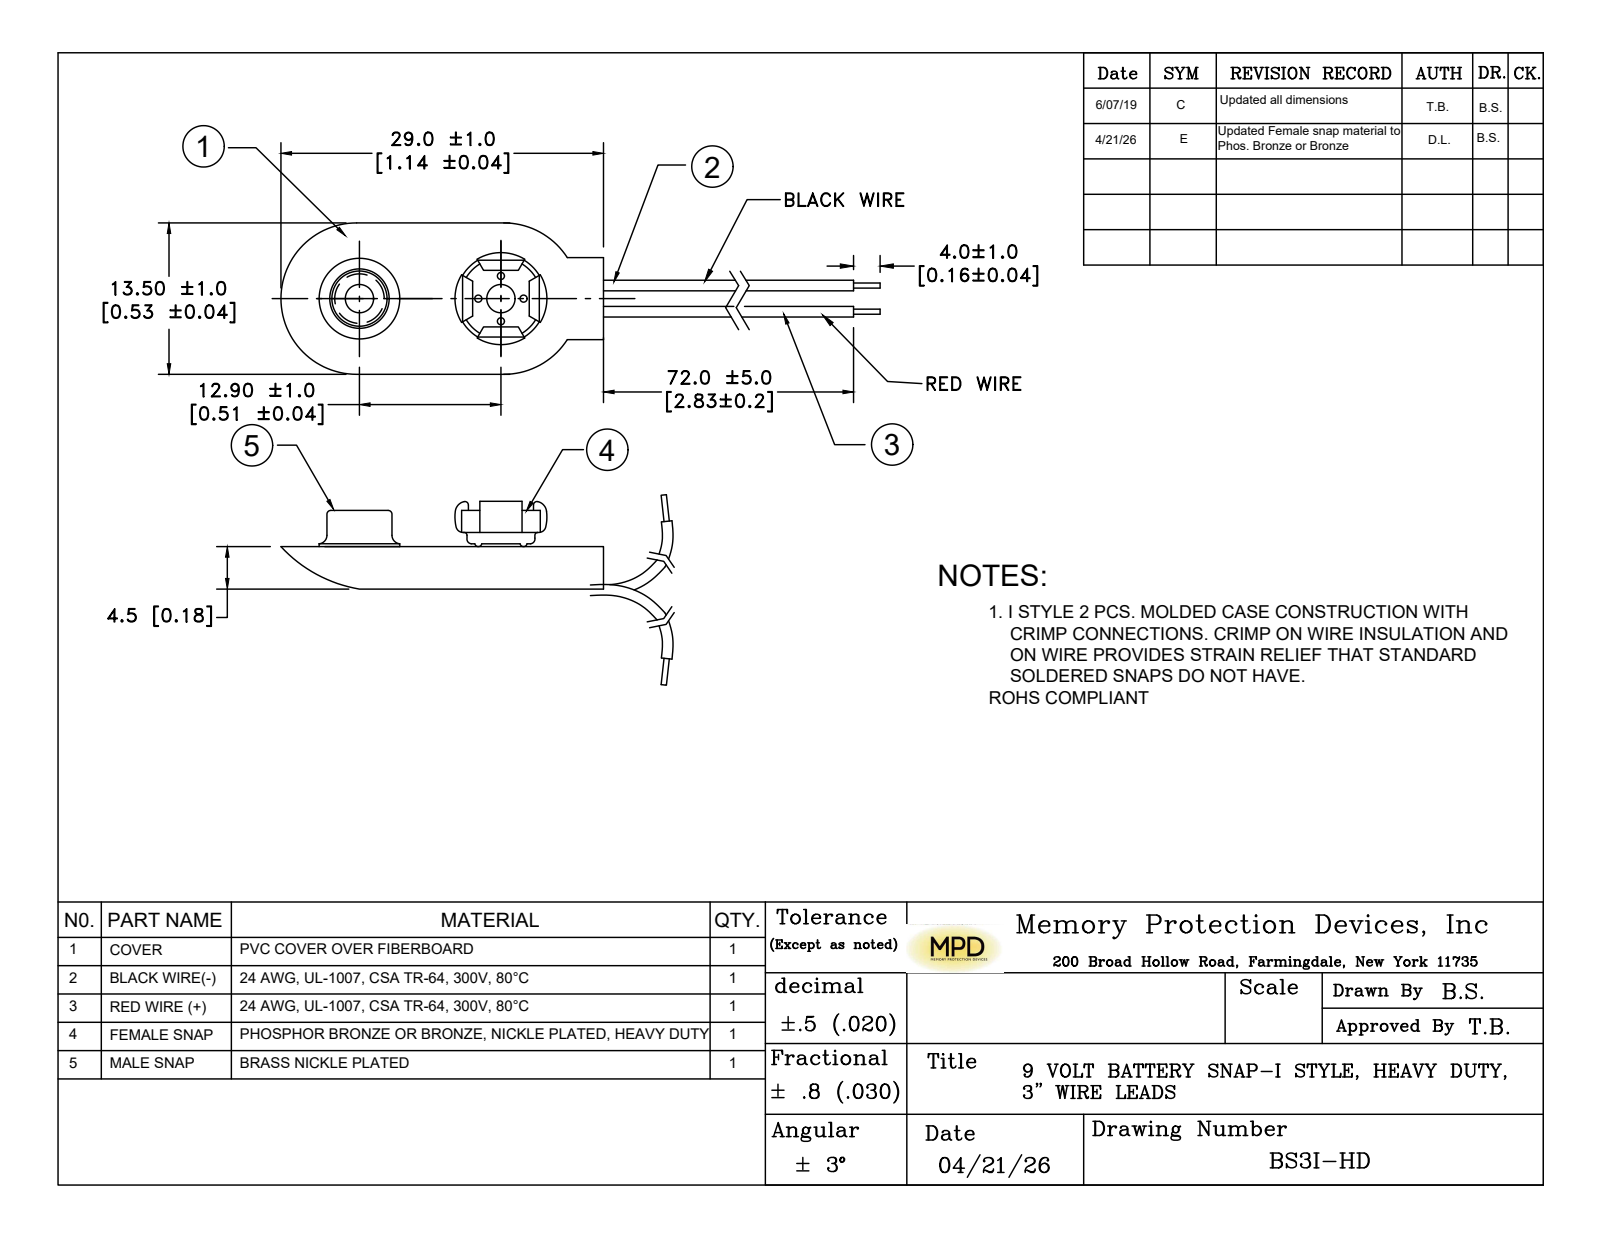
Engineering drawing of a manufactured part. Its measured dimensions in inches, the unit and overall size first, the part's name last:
Units: inches
Overall size (bounding box): 4.134 × 0.531 × 0.333
Round holes (diameter × count): ⌀0.024 ×4, ⌀0.023 ×2, ⌀0.098 ×2, ⌀0.175 ×1, ⌀0.265 ×1
Round bosses / shafts (diameter × count): ⌀0.055 ×2, ⌀0.276 ×1, ⌀0.236 ×1, ⌀0.205 ×1
Partial cylindrical surfaces — rounded edges, fillets, slot ends (radius × count): R0.01 ×4, R0.266 ×2, R0.148 ×1, R0.157 ×1, R0.372 ×1
Main face-to-face distances: 0.177, 0.531, 0.098, 0.433, 0.047, 0.236, 0.059, 0.335, 0.189, 0.224
Hole centre spacings: 0.083, 0.117, 0.165, 0.515, 0.142, 0.425, 0.508, 0.591
Volume: 0.109 in³ · Surface area: 4.027 in²
Bodies: 7 solids, 120 faces (54 planar, 52 cylindrical, 14 other)
Part name (STEP PRODUCT): BS3I
STEP written by: SolidWorks 2017 (AUTOMOTIVE_DESIGN)
